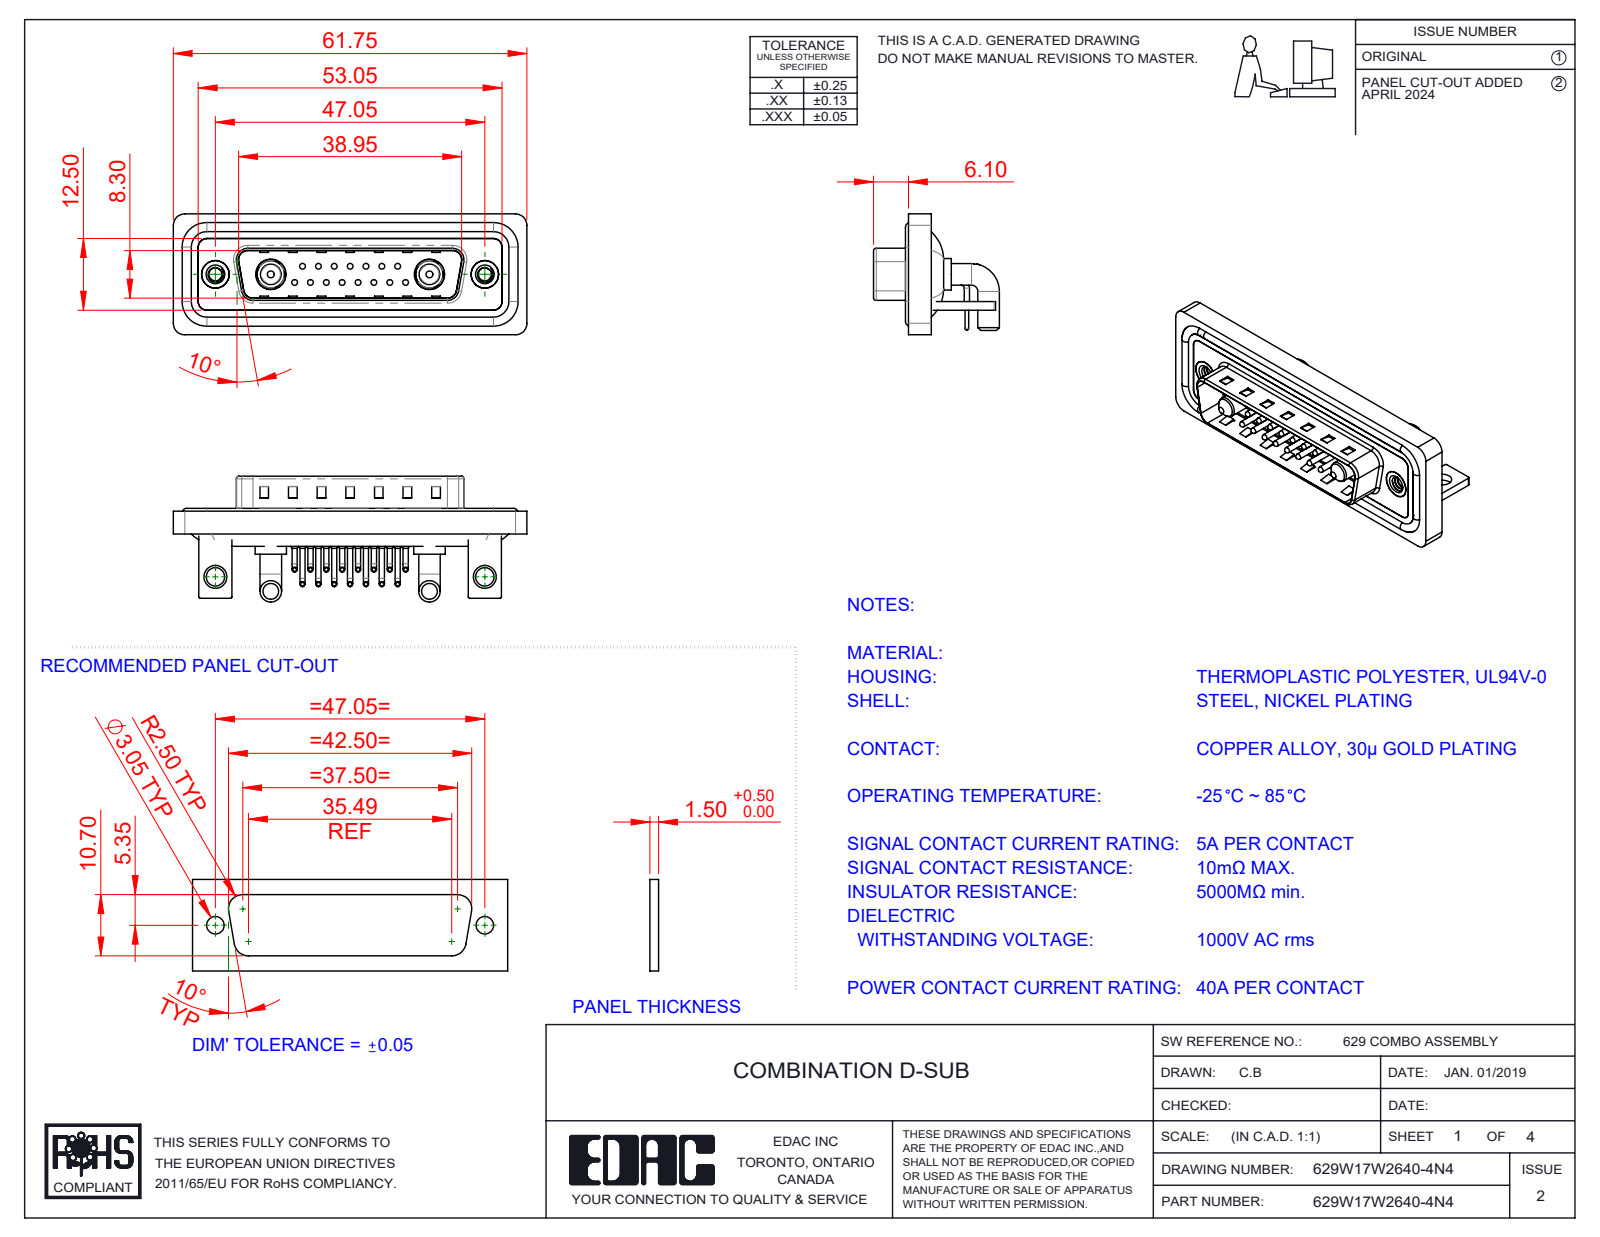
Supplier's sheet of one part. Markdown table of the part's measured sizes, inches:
| quantity | value |
| --- | --- |
| part name | 629Combo Shell Front_25 Contacts; 629Combo Housing_17W2; 629W17W2640-4N4; 629Combo Contact Row 2 (+6 more) |
| STEP written by | SolidWorks 2023 (CONFIG_CONTROL_DESIGN) |
| units | inches |
| bodies | 28 solids, 2259 faces (1209 planar, 788 cylindrical, 262 other) |
| overall size | 2.431 × 0.865 × 0.831 |
| volume | 0.484 in³ |
| surface area | 20.58 in² |
| round holes (diameter × count) | 0.03 × 15, 0.063 × 15, 0.079 × 15, 0.089 × 2, 0.126 × 2, 0.157 × 2, 0.189 × 2, 0.191 × 2, 0.197 × 2, 0.209 × 2 |
| round bosses / shafts (diameter × count) | 0.035 × 30, 0.059 × 15, 0.039 × 15, 0.026 × 15, 0.148 × 4, 0.063 × 4, 0.217 × 2, 0.205 × 2 |
| partial cylindrical surfaces (radius × count) | 0.079 × 19, 0.059 × 18, 0.01 × 16, 0.04 × 15, 0.02 × 9, 0.063 × 8, 0.024 × 4, 0.026 × 4 |
| main face-to-face distances | 0.016, 0.031, 0.083, 0.059, 0.114, 0.043, 0.161, 0.063, 0.177, 0.146 |
| hole center spacings | 0.124, 0.109, 0.218, 0.327, 0.198, 0.295, 0.436, 0.198 |
